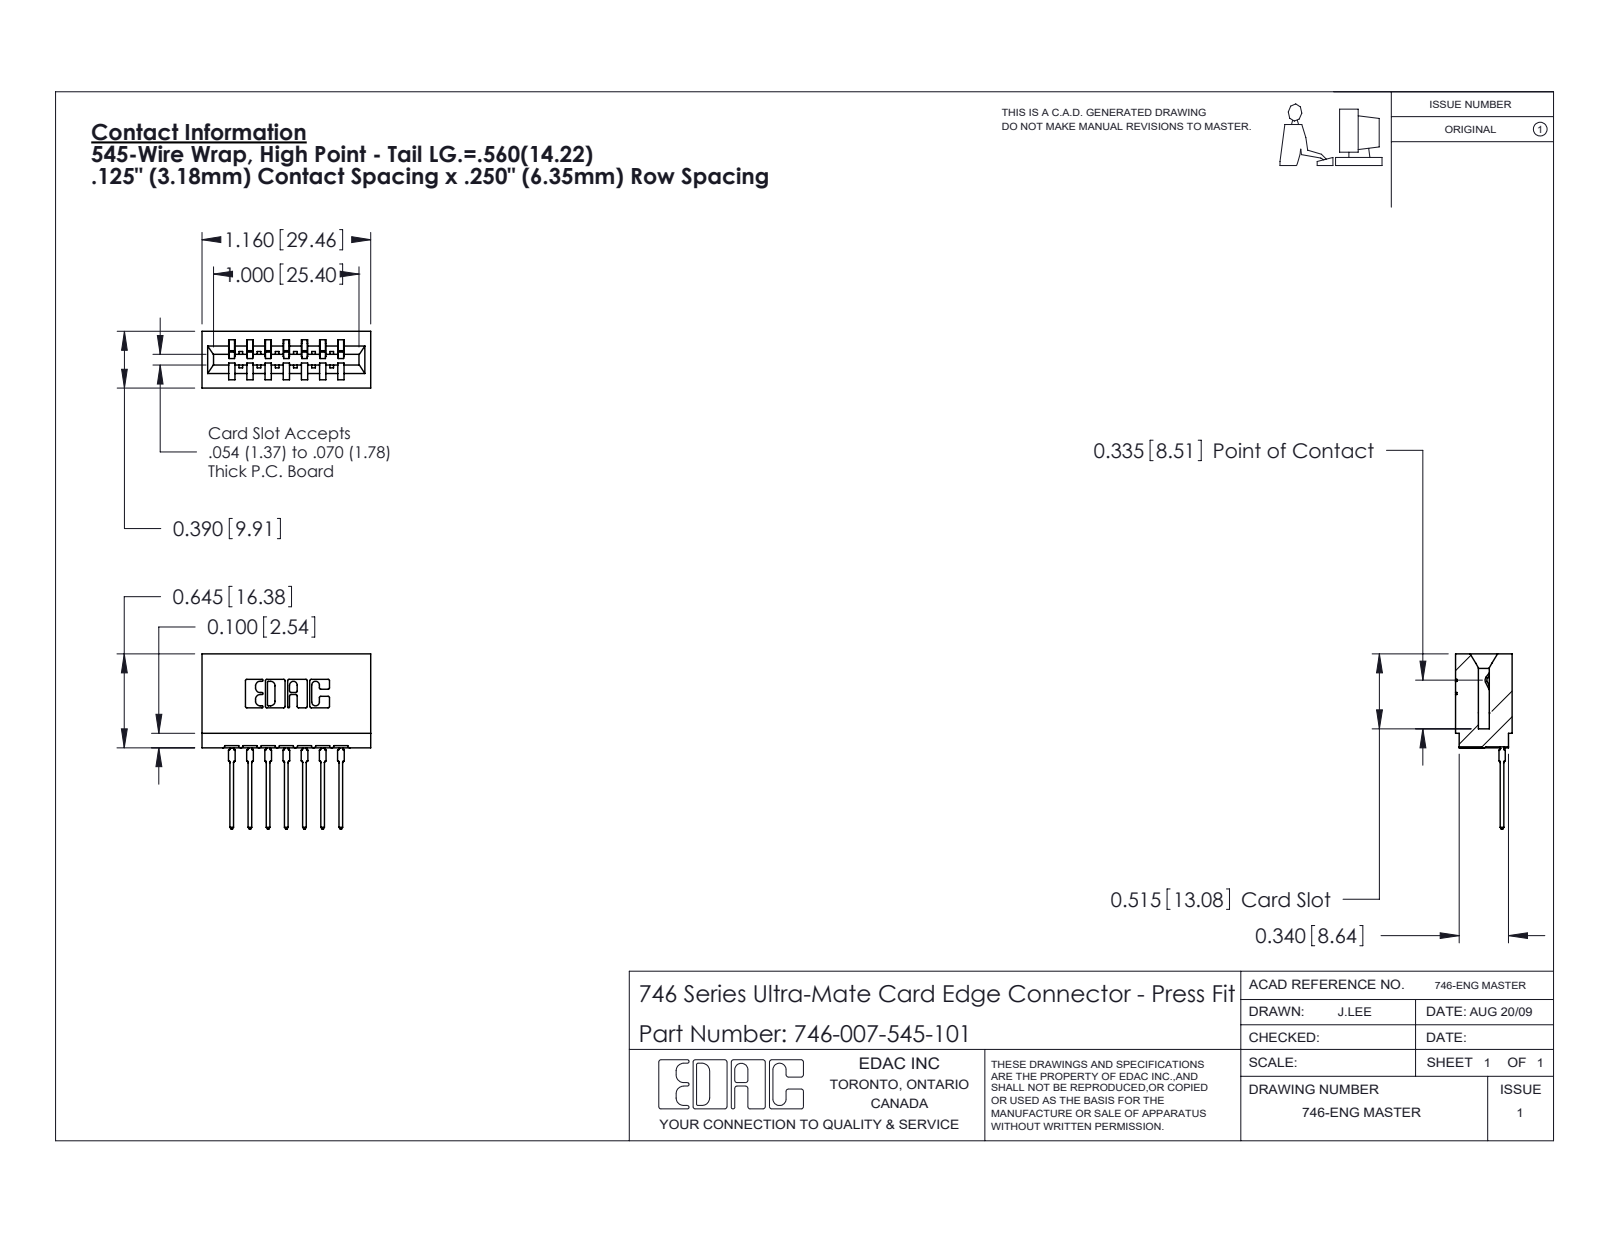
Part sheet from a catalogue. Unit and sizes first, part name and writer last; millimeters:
Units: millimetres
Overall size (bounding box): 30.6 × 29.5 × 9.9
Partial cylindrical surfaces — rounded edges, fillets, slot ends (radius × count): R0.3 ×22, R0.5 ×14, R0.4 ×8, R0.2 ×6, R0.8 ×6, R0.1 ×4, R0.3 ×4, R0.7 ×3
Main face-to-face distances: 6.4, 1.1, 8.5, 3.2, 12.7, 3.2, 1.4, 7.4, 5.3, 9.9
Volume: 3 340 mm³ · Surface area: 4 455 mm²
Bodies: 8 solids, 853 faces (496 planar, 175 cylindrical, 182 other)
Part name (STEP PRODUCT): 746-292-001_545; 746 Part_.515 Slot Depth - 01; 746-007-545-101
STEP written by: SolidWorks 2020 (CONFIG_CONTROL_DESIGN)
